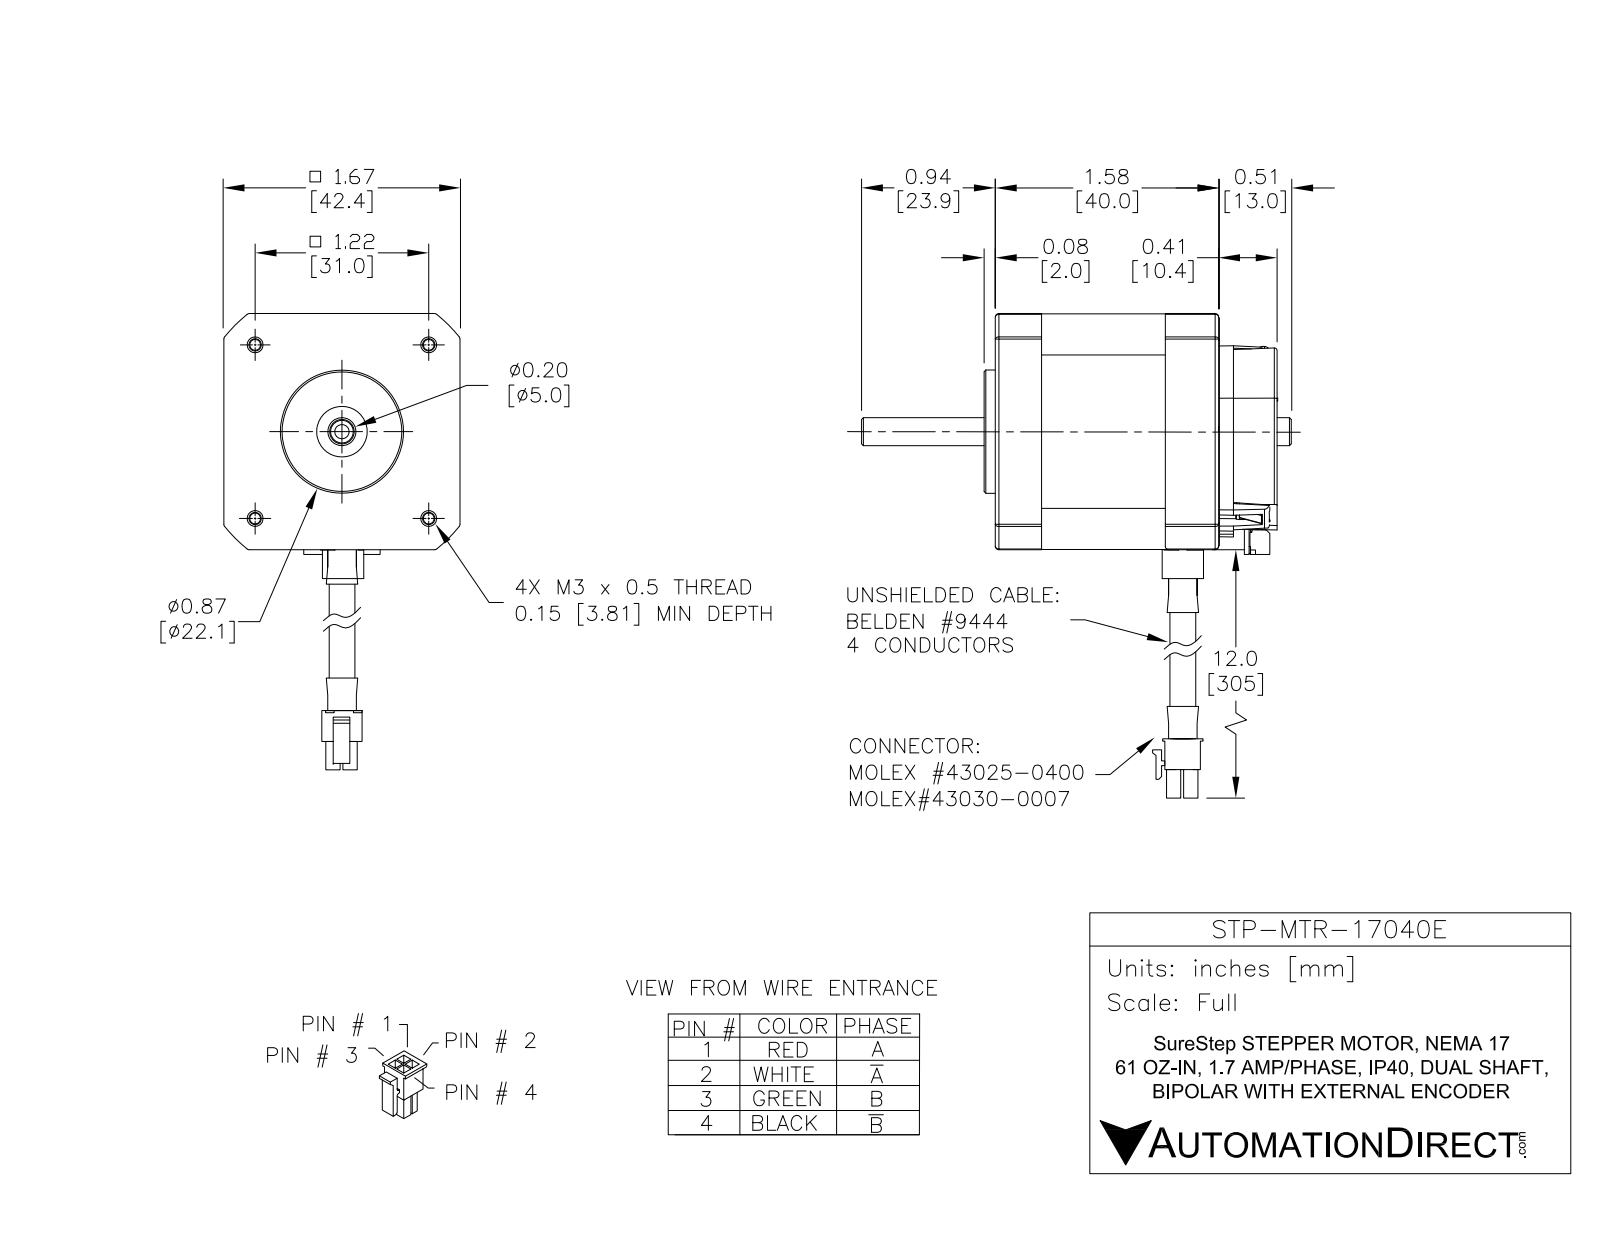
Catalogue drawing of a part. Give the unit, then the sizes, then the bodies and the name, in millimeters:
Units: millimetres
Overall size (bounding box): 355 × 76.7 × 42.2
Round holes (diameter × count): ⌀2 ×6, ⌀0.8 ×4, ⌀0.9 ×4, ⌀2.2 ×4, ⌀3.8 ×4, ⌀1.7 ×2, ⌀2.3 ×2, ⌀2.9 ×2, ⌀4.1 ×2, ⌀4.5 ×2, ⌀1.3 ×1, ⌀6.4 ×1
Round bosses / shafts (diameter × count): ⌀3.3 ×4, ⌀1.5 ×4, ⌀22 ×1, ⌀11.8 ×1, ⌀10.5 ×1, ⌀7.4 ×1, ⌀5.5 ×1, ⌀5 ×1
Partial cylindrical surfaces — rounded edges, fillets, slot ends (radius × count): R1 ×22, R0.6 ×17, R0.5 ×6, R1 ×6, R2 ×6, R0.3 ×4, R0.4 ×4, R2 ×4
Main face-to-face distances: 42.1, 40, 42.1, 42.2, 45.3, 5.3, 4.4, 2.5, 0.8, 44.5
Hole centre spacings: 25.3, 9, 12.7, 18, 25.3, 29.4, 31, 9.2
Volume: 81 940 mm³ · Surface area: 28 210 mm²
Bodies: 15 solids, 1646 faces (967 planar, 392 cylindrical, 287 other)
Part name (STEP PRODUCT): STP-MTR-17040E
STEP written by: SolidWorks 2017 (AUTOMOTIVE_DESIGN)
